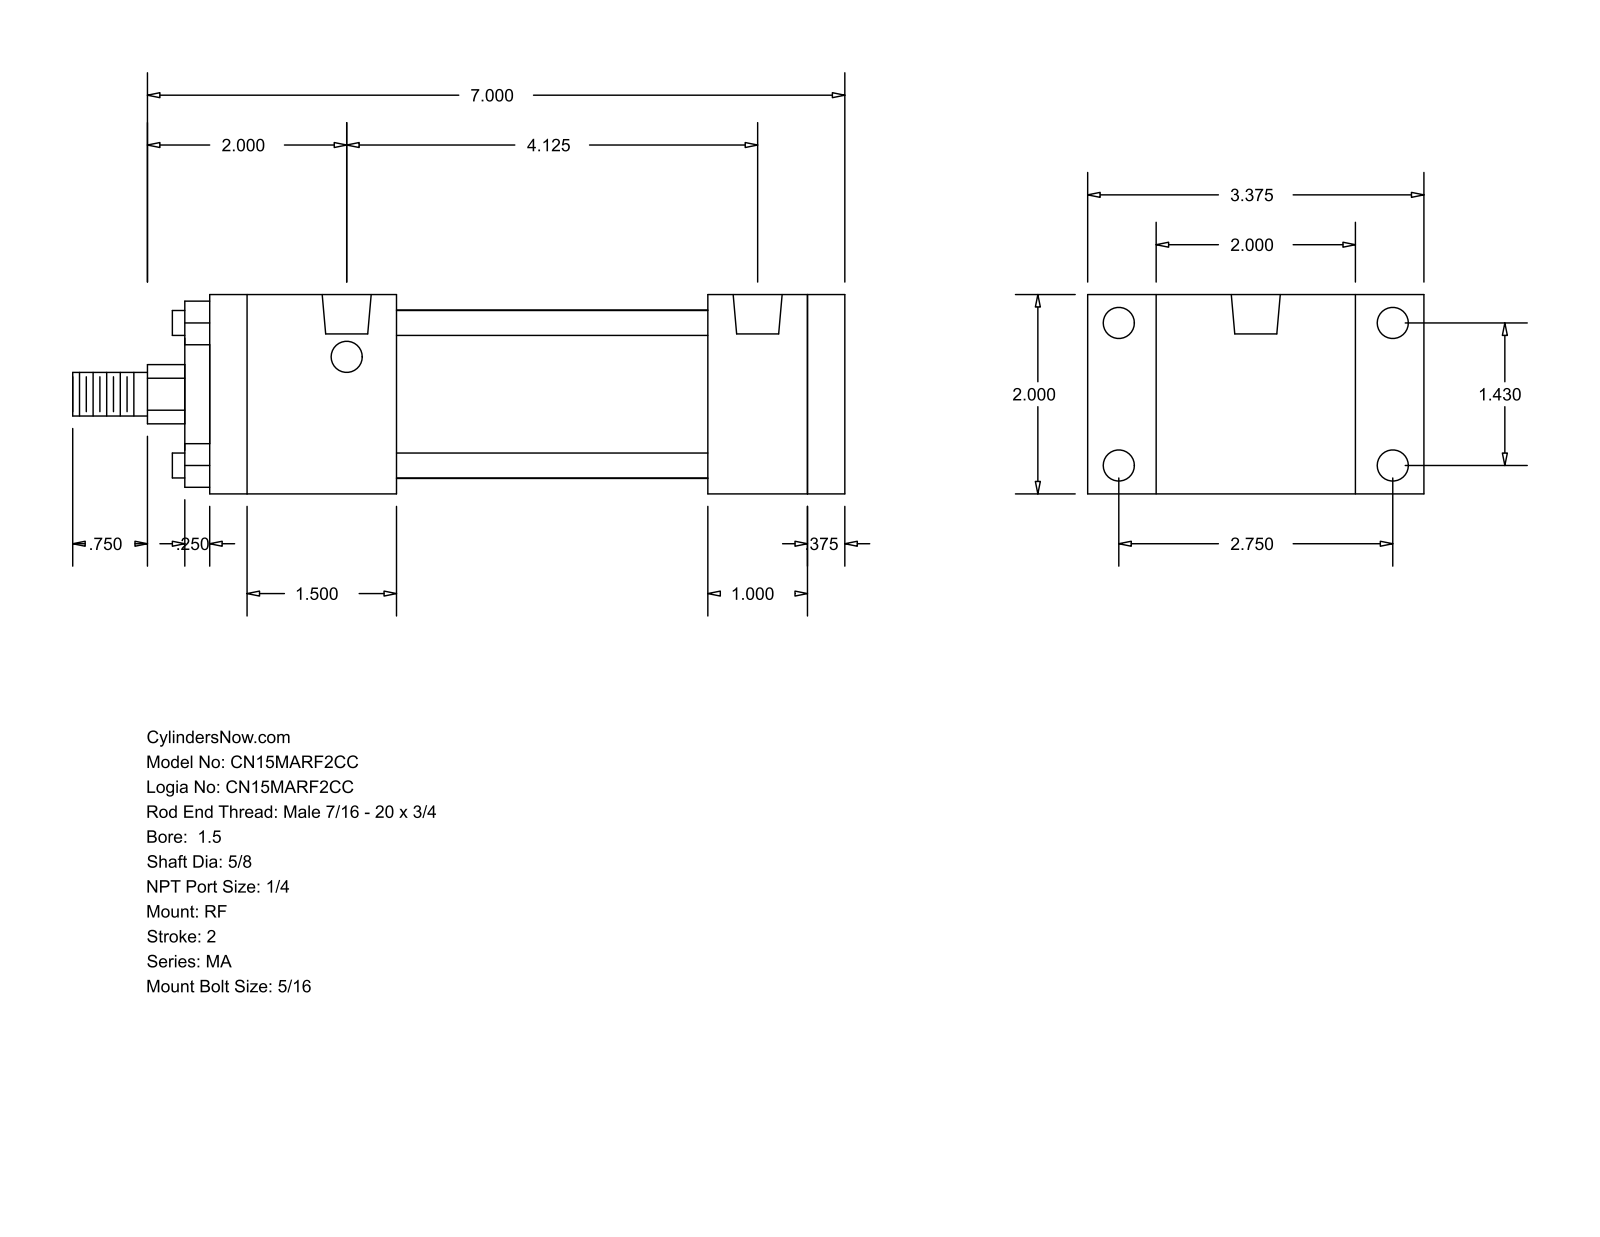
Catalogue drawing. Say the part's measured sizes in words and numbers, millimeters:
The part is named "MA_RF__0150_0.625". Its 3-D file was written by "GSSL Pune (CONFIG_CONTROL_DESIGN)". It is 0 solids with 92 faces: 64 planar, 28 cylindrical and 0 other. Overall it measures 196.85 by 85.72 by 50.8 millimeters. Round holes: 8 of diameter 7.94, 2 of diameter 12.49. Round bosses or shafts: 4 of diameter 6.35, 1 of diameter 42.93, 1 of diameter 28.57, 1 of diameter 15.88, 1 of diameter 11.11. Partial cylindrical surfaces (rounded edges, fillets, slot ends): 1 of radius 7.54. The main face-to-face distances are 50.8, 9.52, 152.4, 161.92, 25.4, 127, 34.92, 47.62, 79.38, 104.78. The hole center spacings are 36.32, 69.84, 78.72, 104.77.
